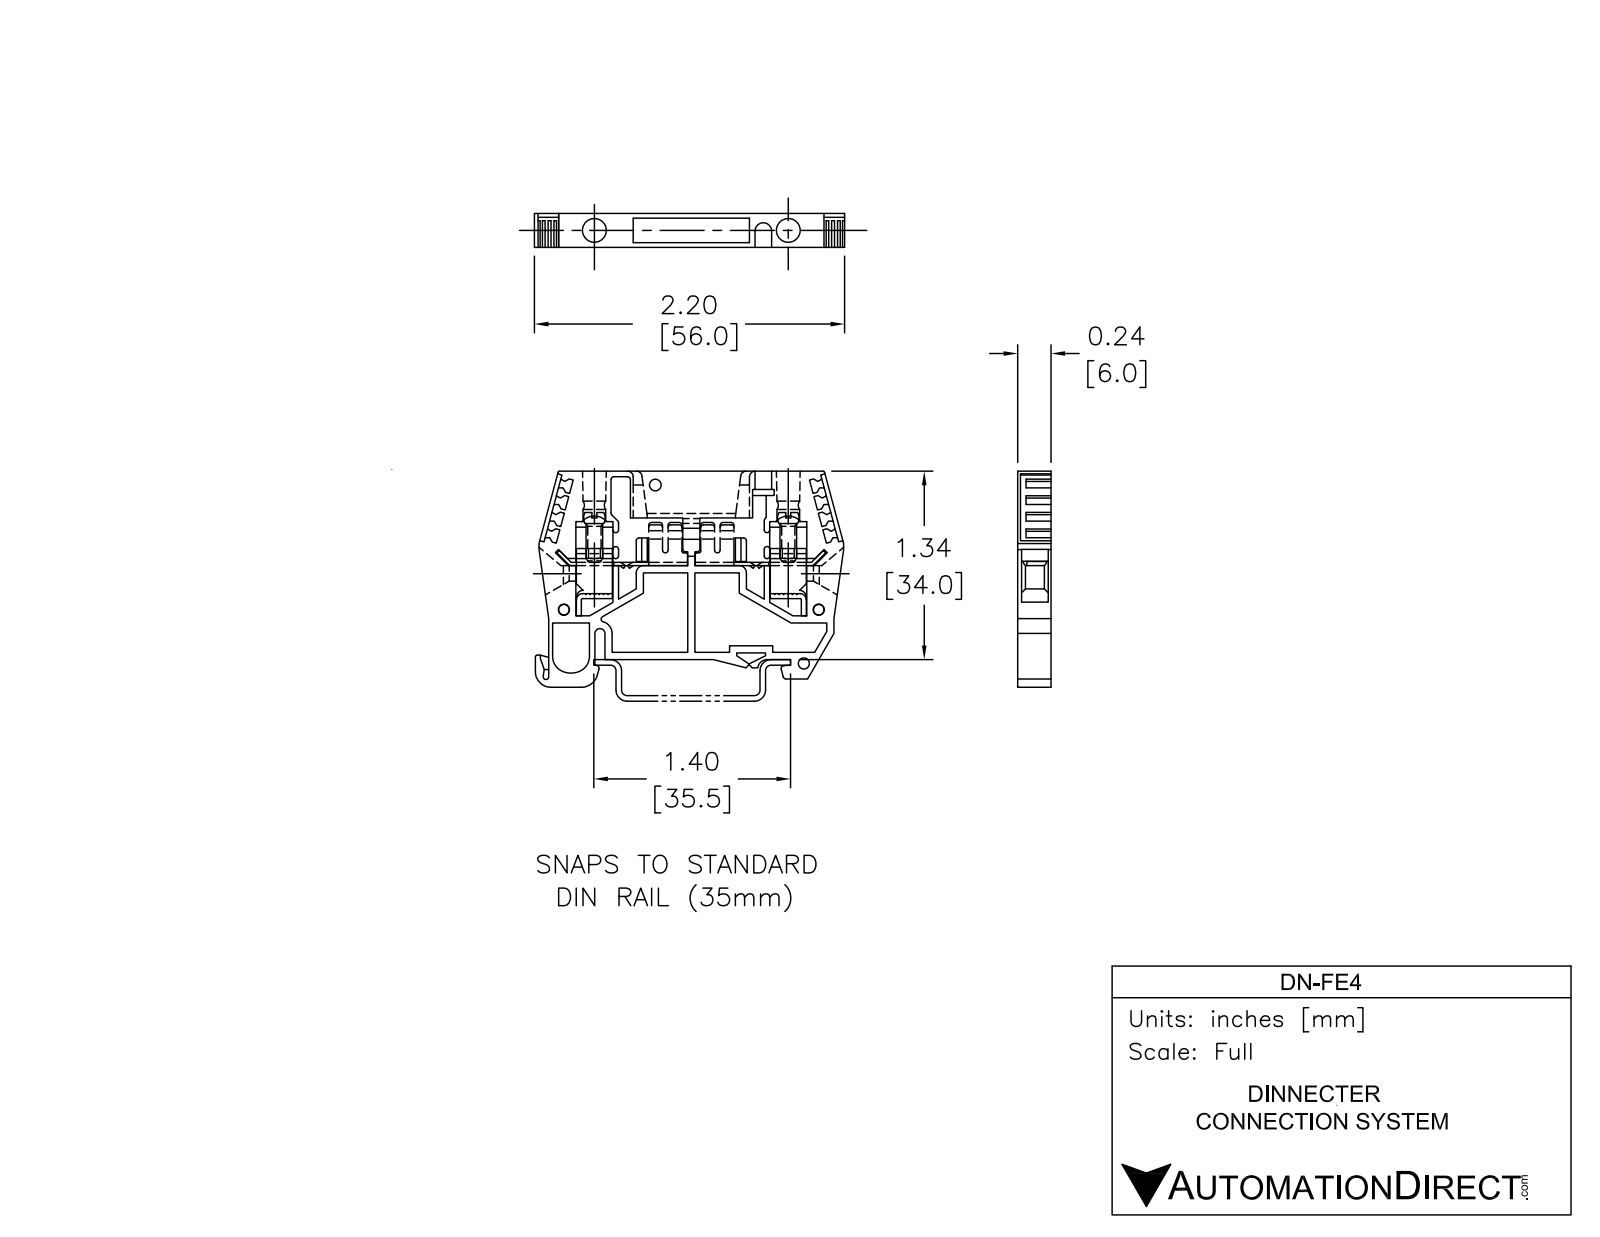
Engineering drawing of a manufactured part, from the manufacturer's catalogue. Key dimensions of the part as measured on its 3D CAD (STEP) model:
Part name (STEP PRODUCT): 4358100_DN-QFE4
STEP written by: SolidWorks 2013 (AUTOMOTIVE_DESIGN)
Units: millimetres
Bodies: 1 solid, 314 faces (223 planar, 67 cylindrical, 24 other)
Overall size (bounding box): 55.65 × 39 × 6
Volume: 8 980 mm³ · Surface area: 6 582 mm²
Round holes (diameter × count): ⌀2 ×3, ⌀4.1 ×2
Partial cylindrical surfaces — rounded edges, fillets, slot ends (radius × count): R0.5 ×13, R3 ×5, R1 ×3, R1.3 ×2, R1.5 ×2, R0.9 ×1, R1.05 ×1, R1.7 ×1
Main face-to-face distances: 6, 0.5, 3.5, 2, 2.5, 5.5, 34, 2.2, 1.5, 3
Hole centre spacings: 10.07, 35, 44.38, 46
